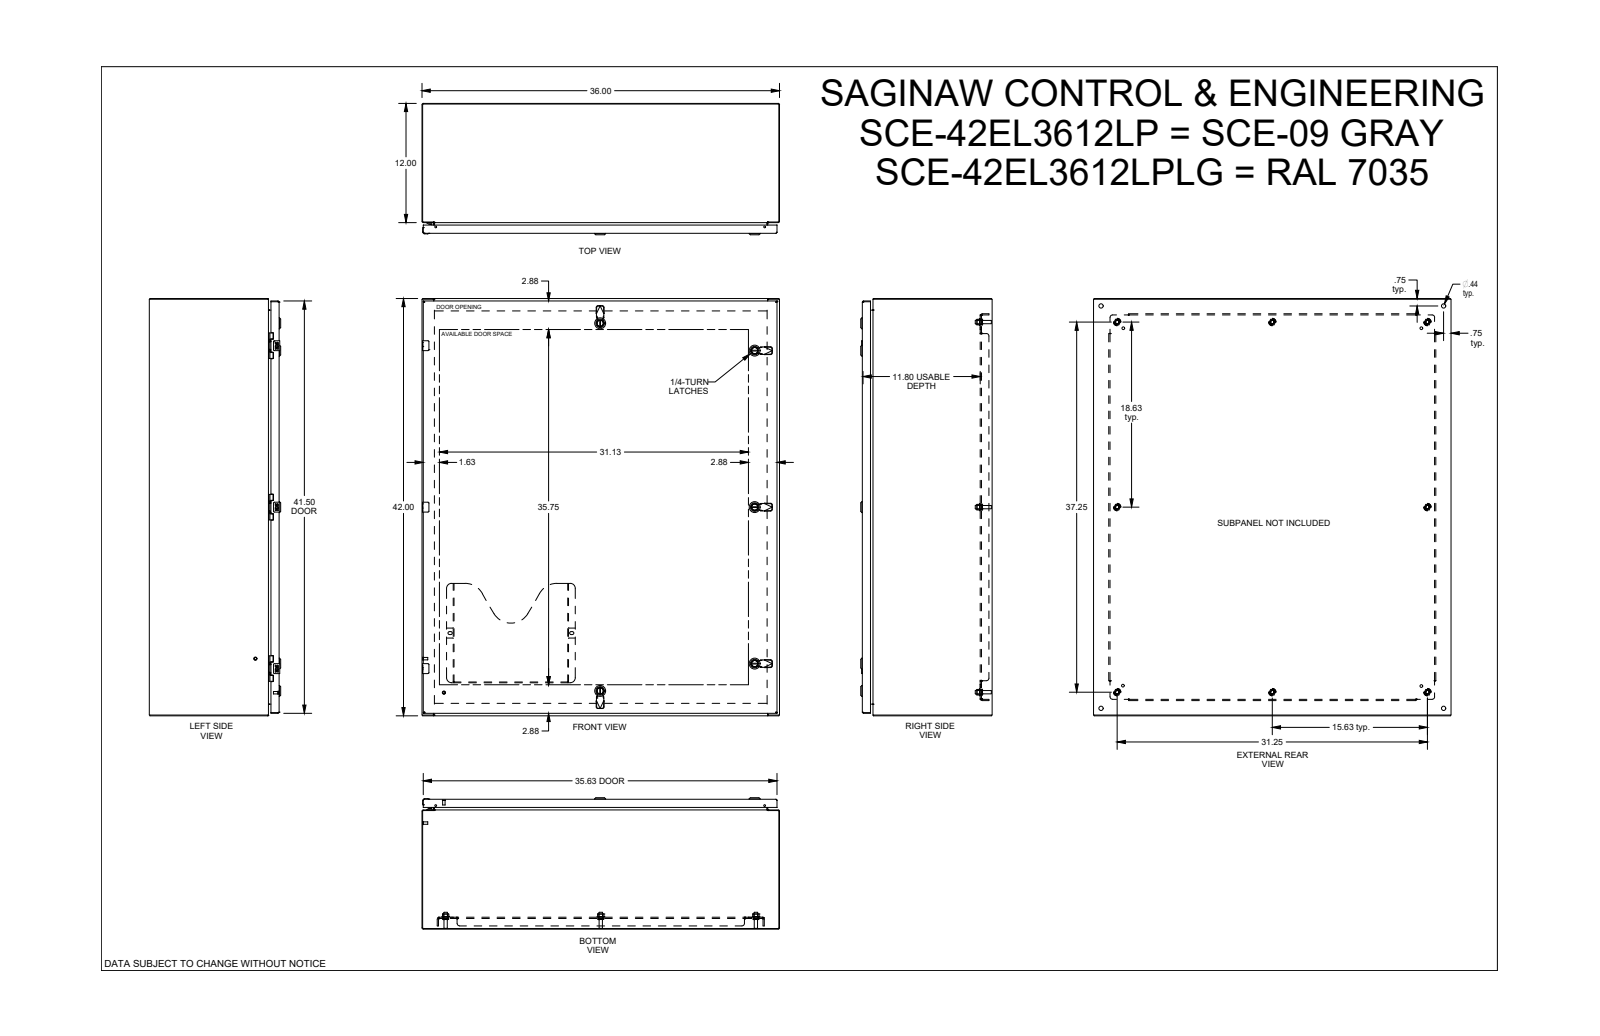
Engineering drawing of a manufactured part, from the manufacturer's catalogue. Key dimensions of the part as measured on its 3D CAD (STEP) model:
Part name (STEP PRODUCT): SCE-42EL3612LP
STEP written by: SolidWorks 2019 (CONFIG_CONTROL_DESIGN)
Units: inches
Bodies: 0 solids, 4774 faces (2327 planar, 1328 cylindrical, 1119 other)
Overall size (bounding box): 42 × 36 × 13.23
Round holes (diameter × count): ⌀0.367 ×8, ⌀0.5 ×8, ⌀0.172 ×6, ⌀0.205 ×6, ⌀0.244 ×6, ⌀0.266 ×6, ⌀0.375 ×6, ⌀0.197 ×5, ⌀0.315 ×5, ⌀0.394 ×5, ⌀0.634 ×5, ⌀0.281 ×4
Round bosses / shafts (diameter × count): ⌀0.17 ×9, ⌀0.366 ×8, ⌀0.332 ×8, ⌀0.25 ×6, ⌀0.24 ×6, ⌀1.102 ×5, ⌀0.866 ×5, ⌀0.802 ×5
Partial cylindrical surfaces — rounded edges, fillets, slot ends (radius × count): R0.012 ×136, R0.01 ×52, R0.02 ×52, R0.015 ×32, R0.157 ×20, R0.04 ×17, R0.025 ×16, R0.1 ×16
Main face-to-face distances: 0.075, 0.075, 12.923, 12.998, 13.073, 12.998, 1.2, 11.873, 1, 1.125
Hole centre spacings: 16.25, 0.985, 32.5, 0.02, 0.493, 0.494, 4.493, 15.265
